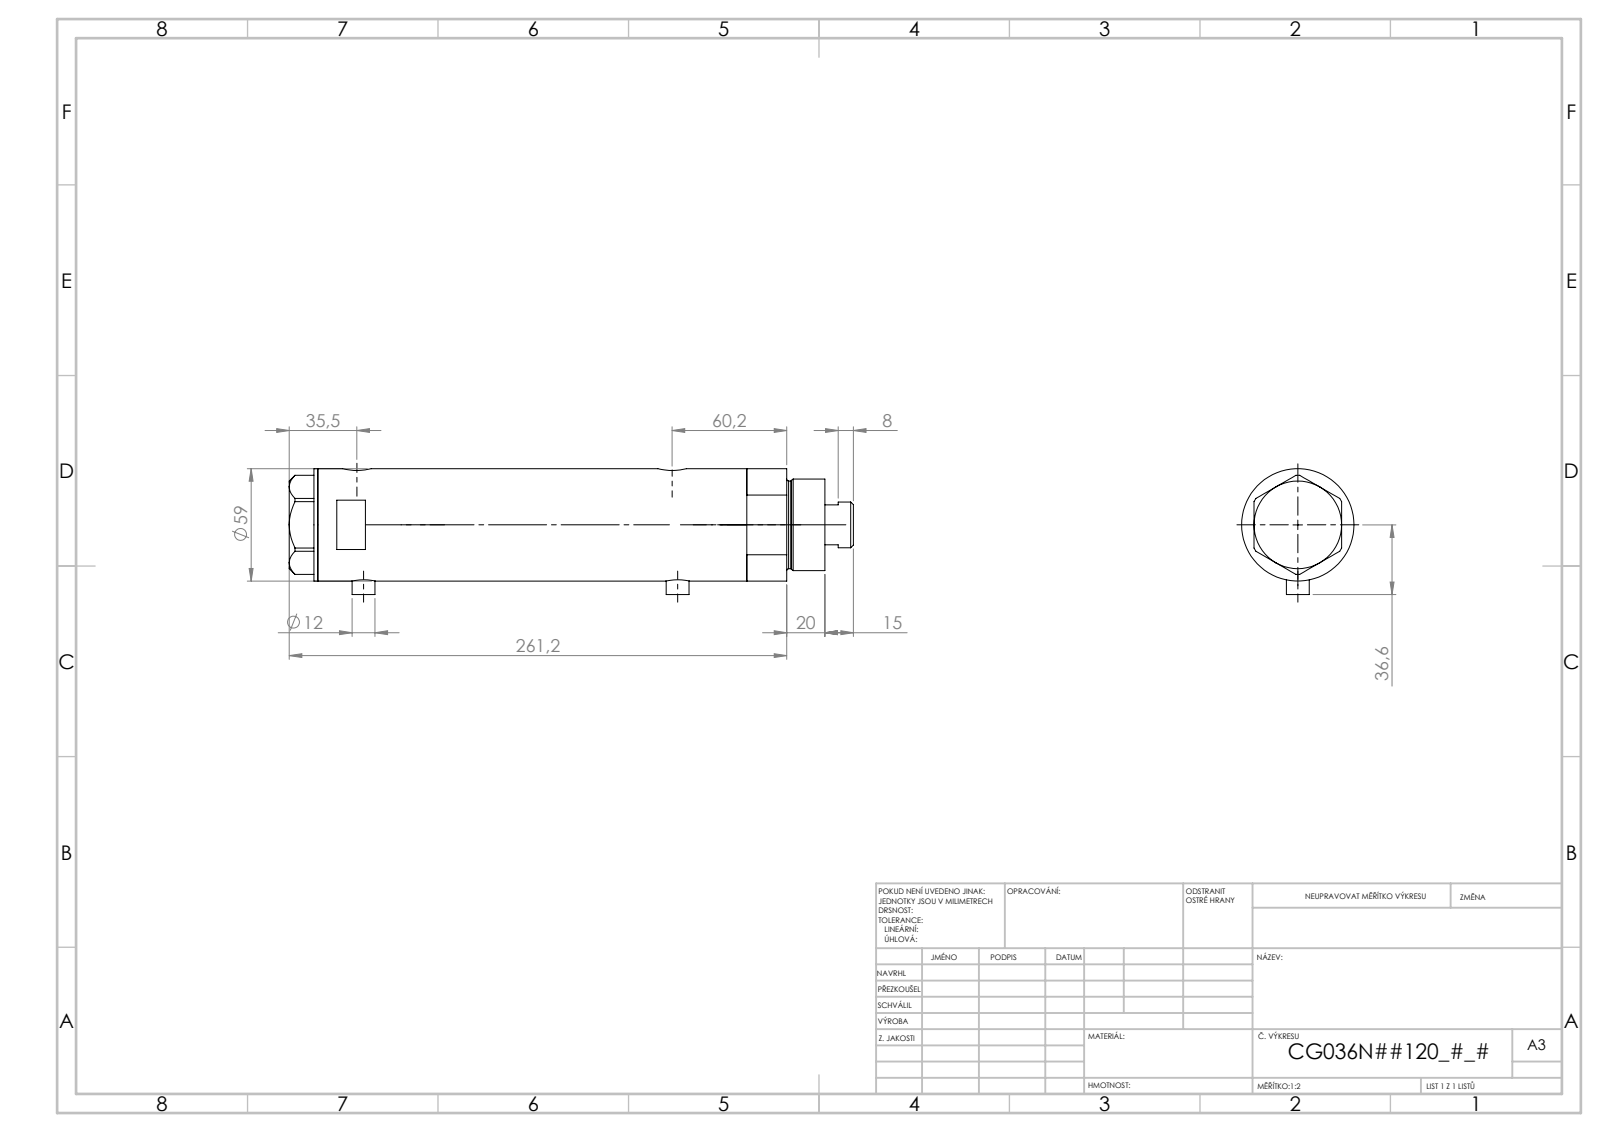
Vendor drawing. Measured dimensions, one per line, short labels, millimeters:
name: V270CG_FRONT; V270CG_MIDDLE; V270CG_VC; V270CG_BACK
written by: SolidWorks 2019 (CONFIG_CONTROL_DESIGN)
unit: mm
bodies: 4 solids, 126 faces (53 planar, 53 cylindrical, 20 other)
size: 283.42 × 60.1 × 59
volume: 635 978 mm³; area: 127 132 mm²
holes: 2× ⌀5, 2× ⌀9.73, 2× ⌀12.5, 2× ⌀15, 1× ⌀8.5, 1× ⌀25, 1× ⌀26.5, 1× ⌀36, 1× ⌀40, 1× ⌀52
bosses: 2× ⌀12, 1× ⌀59, 1× ⌀48, 1× ⌀46, 1× ⌀24
face distances: 177.34, 23.5, 153.84, 15, 38.5, 192.34, 268.42, 253.42, 229.92, 76.08
hole spacings: 2.9, 3.5, 152.15, 155.05, 155.65, 158.55, 2.89, 2.91
